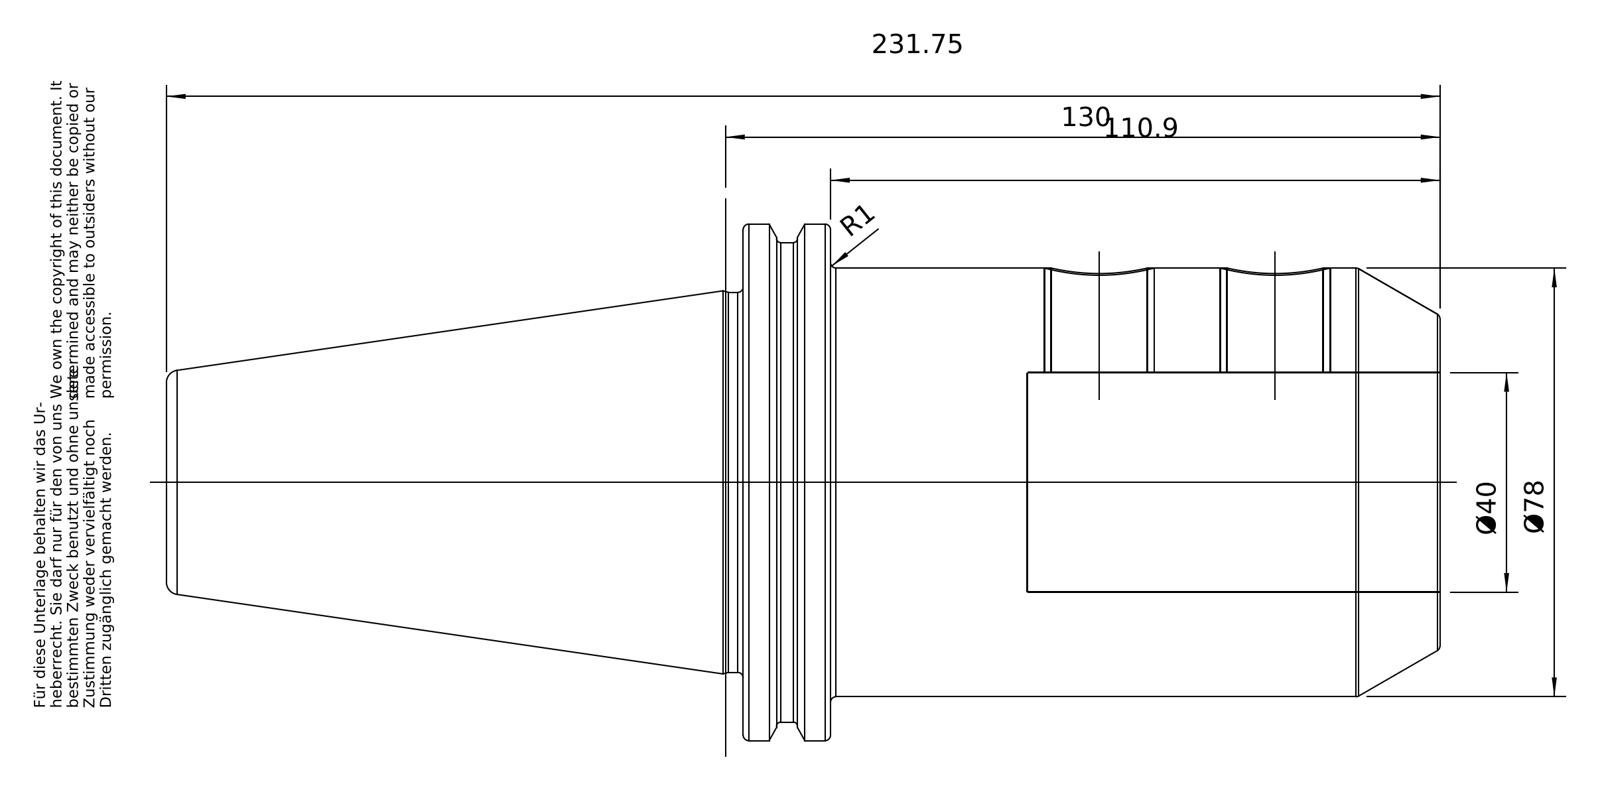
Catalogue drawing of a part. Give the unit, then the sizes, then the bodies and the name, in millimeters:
Units: millimetres
Overall size (bounding box): 231.6 × 97.47 × 94
Round holes (diameter × count): ⌀17.5 ×2, ⌀20 ×2, ⌀20.75 ×1, ⌀25.01 ×1, ⌀25.7 ×1, ⌀40 ×1
Round bosses / shafts (diameter × count): ⌀91 ×1, ⌀78 ×1, ⌀69.15 ×1, ⌀24.01 ×1
Partial cylindrical surfaces — rounded edges, fillets, slot ends (radius × count): R1.75 ×5, R48.74 ×1
Main face-to-face distances: 15.85, 126.8, 110.95, 51.7, 35.85, 75.1, 72.8, 104.8, 120.65, 156.5
Hole centre spacings: 32
Volume: 749 832 mm³ · Surface area: 81 201 mm²
Bodies: 1 solid, 109 faces (24 planar, 36 cylindrical, 49 other)
Part name (STEP PRODUCT): 50-304-40
STEP written by: PRO/ENGINEER BY PARAMETRIC TECHNOLOGY CORPORATION, 2010430 (CONFIG_CONTROL_DESIGN)
